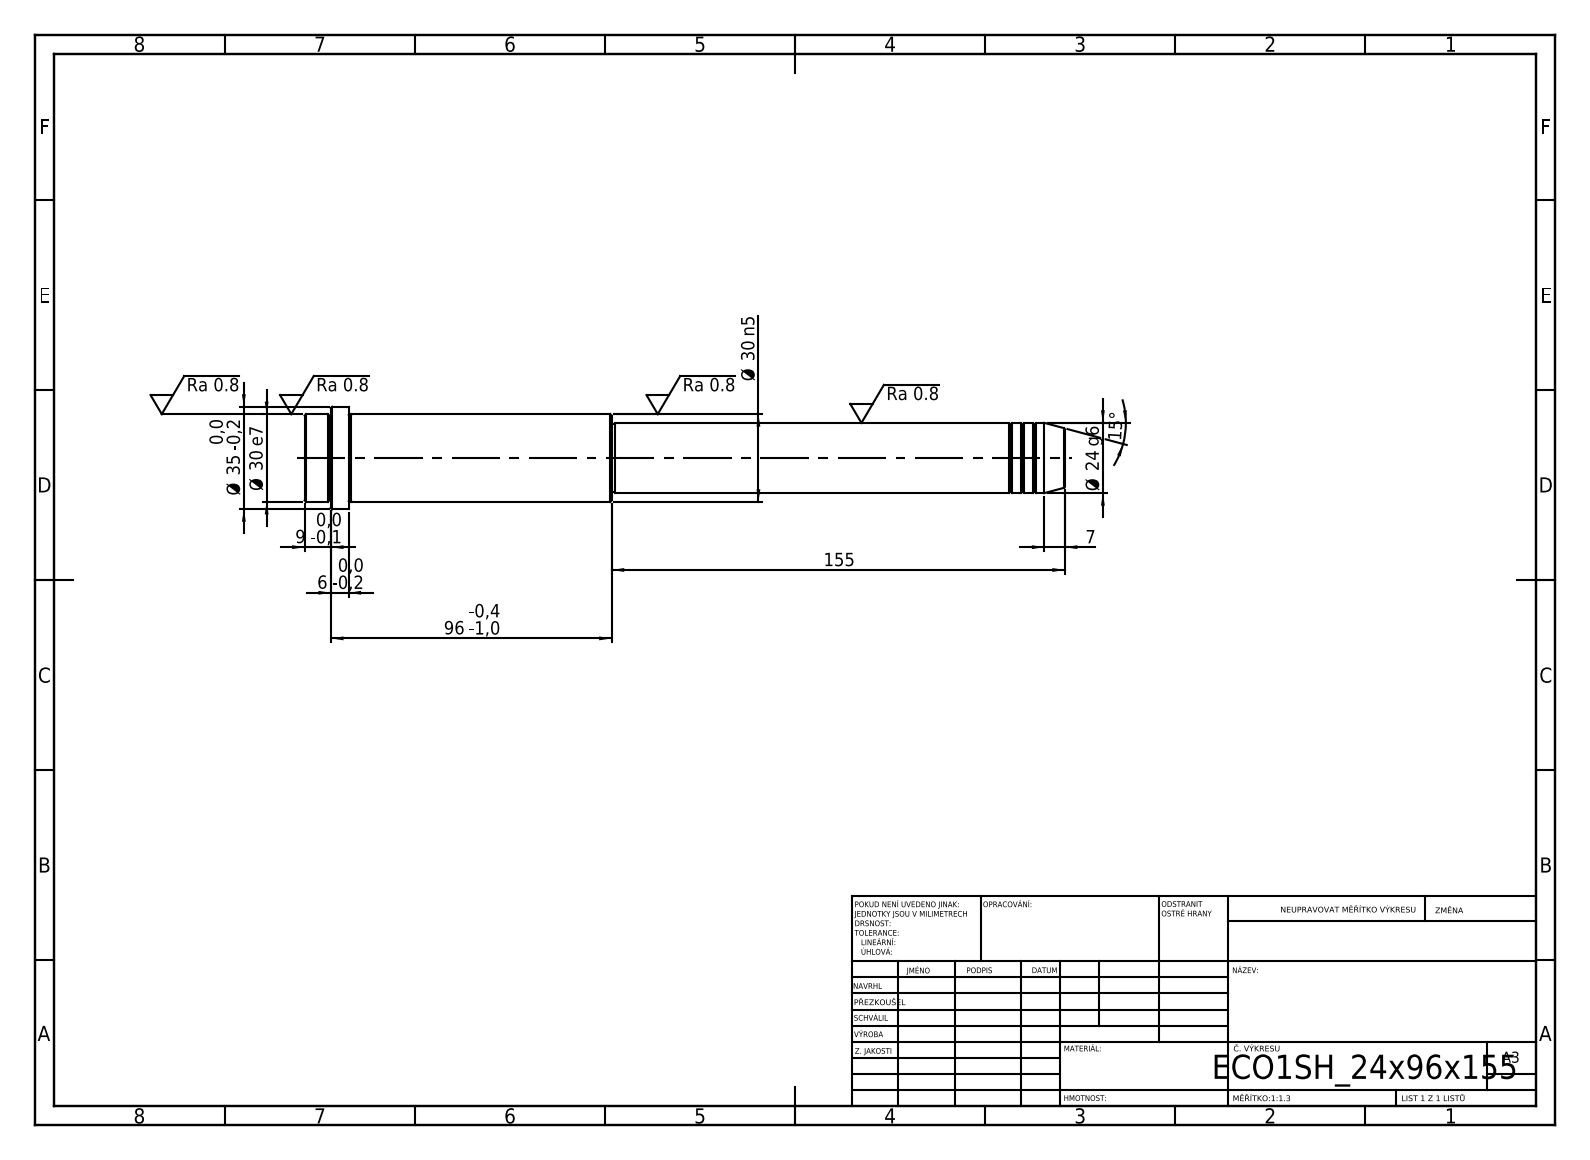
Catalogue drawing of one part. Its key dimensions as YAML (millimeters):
step_written_by: "SolidWorks 2019 (CONFIG_CONTROL_DESIGN)"
units: millimeters
bodies: {solids: 1, faces: 52, planar: 6, cylindrical: 16, other: 30}
overall_size: [260, 35, 35]
volume: 145167
surface_area: 23643
round_bosses_or_shafts:
  - {diameter: 35, count: 1}
  - {diameter: 30, count: 1}
  - {diameter: 24, count: 1}
  - {diameter: 23, count: 1}
face_to_face_distances: [260, 245, 15, 155, 90, 105, 251, 96, 6, 9]
